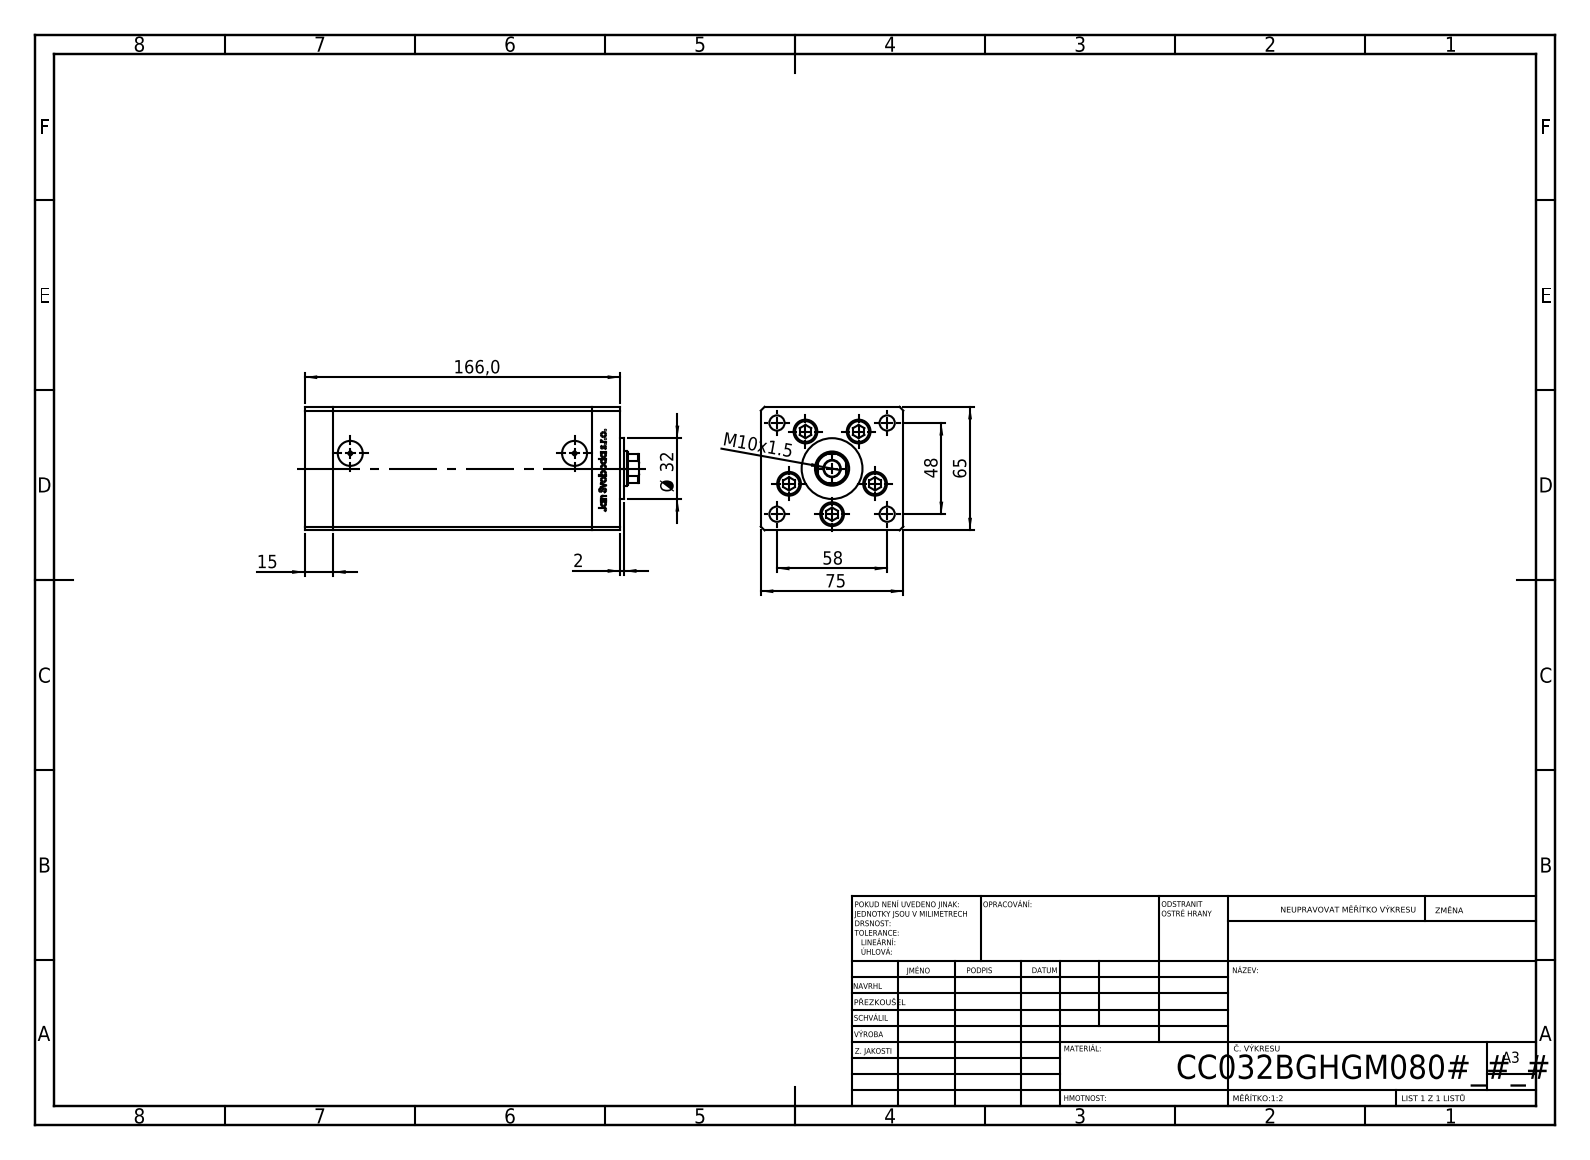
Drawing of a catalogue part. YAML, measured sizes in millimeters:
part_name: "V220C_B MIDDLE; V220C_VC_B; V220C_FRONT_B; ALLEN BOLT (+1 more)"
step_written_by: "SolidWorks 2019 (CONFIG_CONTROL_DESIGN)"
units: millimeters
bodies: {solids: 14, faces: 1183, planar: 462, cylindrical: 147, other: 574}
overall_size: [176, 75, 65]
volume: 722505
surface_area: 127353
round_holes:
  - {diameter: 9, count: 5}
  - {diameter: 12.5, count: 5}
  - {diameter: 8, count: 4}
  - {diameter: 2, count: 2}
  - {diameter: 13.16, count: 2}
  - {diameter: 8.5, count: 1}
  - {diameter: 18, count: 1}
round_bosses_or_shafts:
  - {diameter: 8, count: 5}
  - {diameter: 32, count: 1}
partial_cylinders:
  - {radius: 0.93, count: 2}
  - {radius: 8.5, count: 1}
face_to_face_distances: [75, 65, 15, 136, 151, 166, 28, 13, 54.5, 10.5]
hole_center_spacings: [24, 37.64, 15.67, 17.22, 27.71, 28.83, 29, 32.63]
